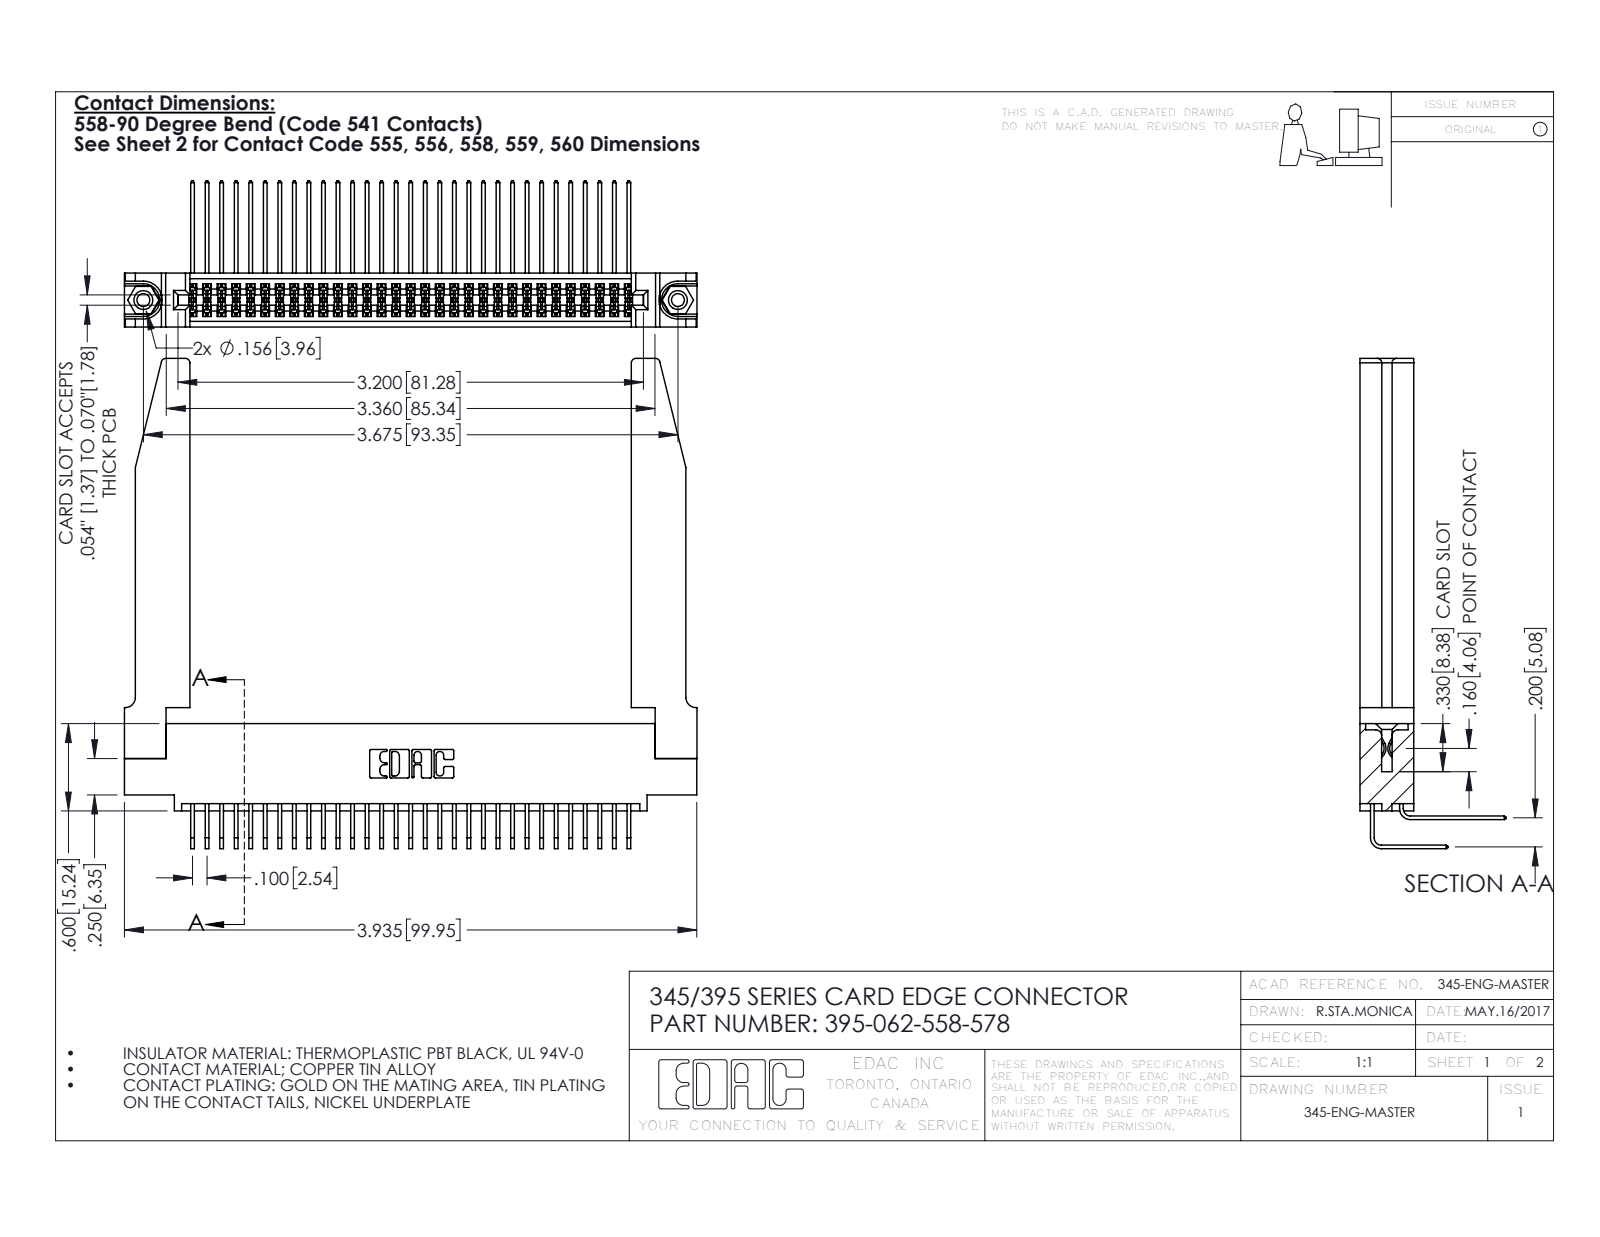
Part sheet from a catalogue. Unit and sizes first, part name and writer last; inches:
Units: inches
Overall size (bounding box): 3.936 × 3.369 × 1.005
Round holes (diameter × count): ⌀0.089 ×2, ⌀0.125 ×2, ⌀0.156 ×2, ⌀0.064 ×1
Round bosses / shafts (diameter × count): ⌀0.155 ×2
Partial cylindrical surfaces — rounded edges, fillets, slot ends (radius × count): R0.006 ×94, R0.01 ×22, R0.03 ×8, R0.007 ×6, R0.031 ×6, R0.026 ×3, R0.014 ×2, R0.019 ×2
Main face-to-face distances: 0.37, 0.072, 0.298, 0.2, 0.098, 0.272, 0.025, 0.225, 0.15, 0.148
Hole centre spacings: 0.27, 3.44, 3.675
Volume: 1.078 in³ · Surface area: 35.69 in²
Bodies: 67 solids, 3588 faces (2396 planar, 1140 cylindrical, 52 other)
Part name (STEP PRODUCT): 345-292-001_558 Tail - 2; 345-292-001_558 559 Tail - 1; 345-250-001_345-250-001-102; 345 Part_0.110 Offset - 0.156 Dia-TH (+2 more)
STEP written by: SolidWorks 2016 (CONFIG_CONTROL_DESIGN)
